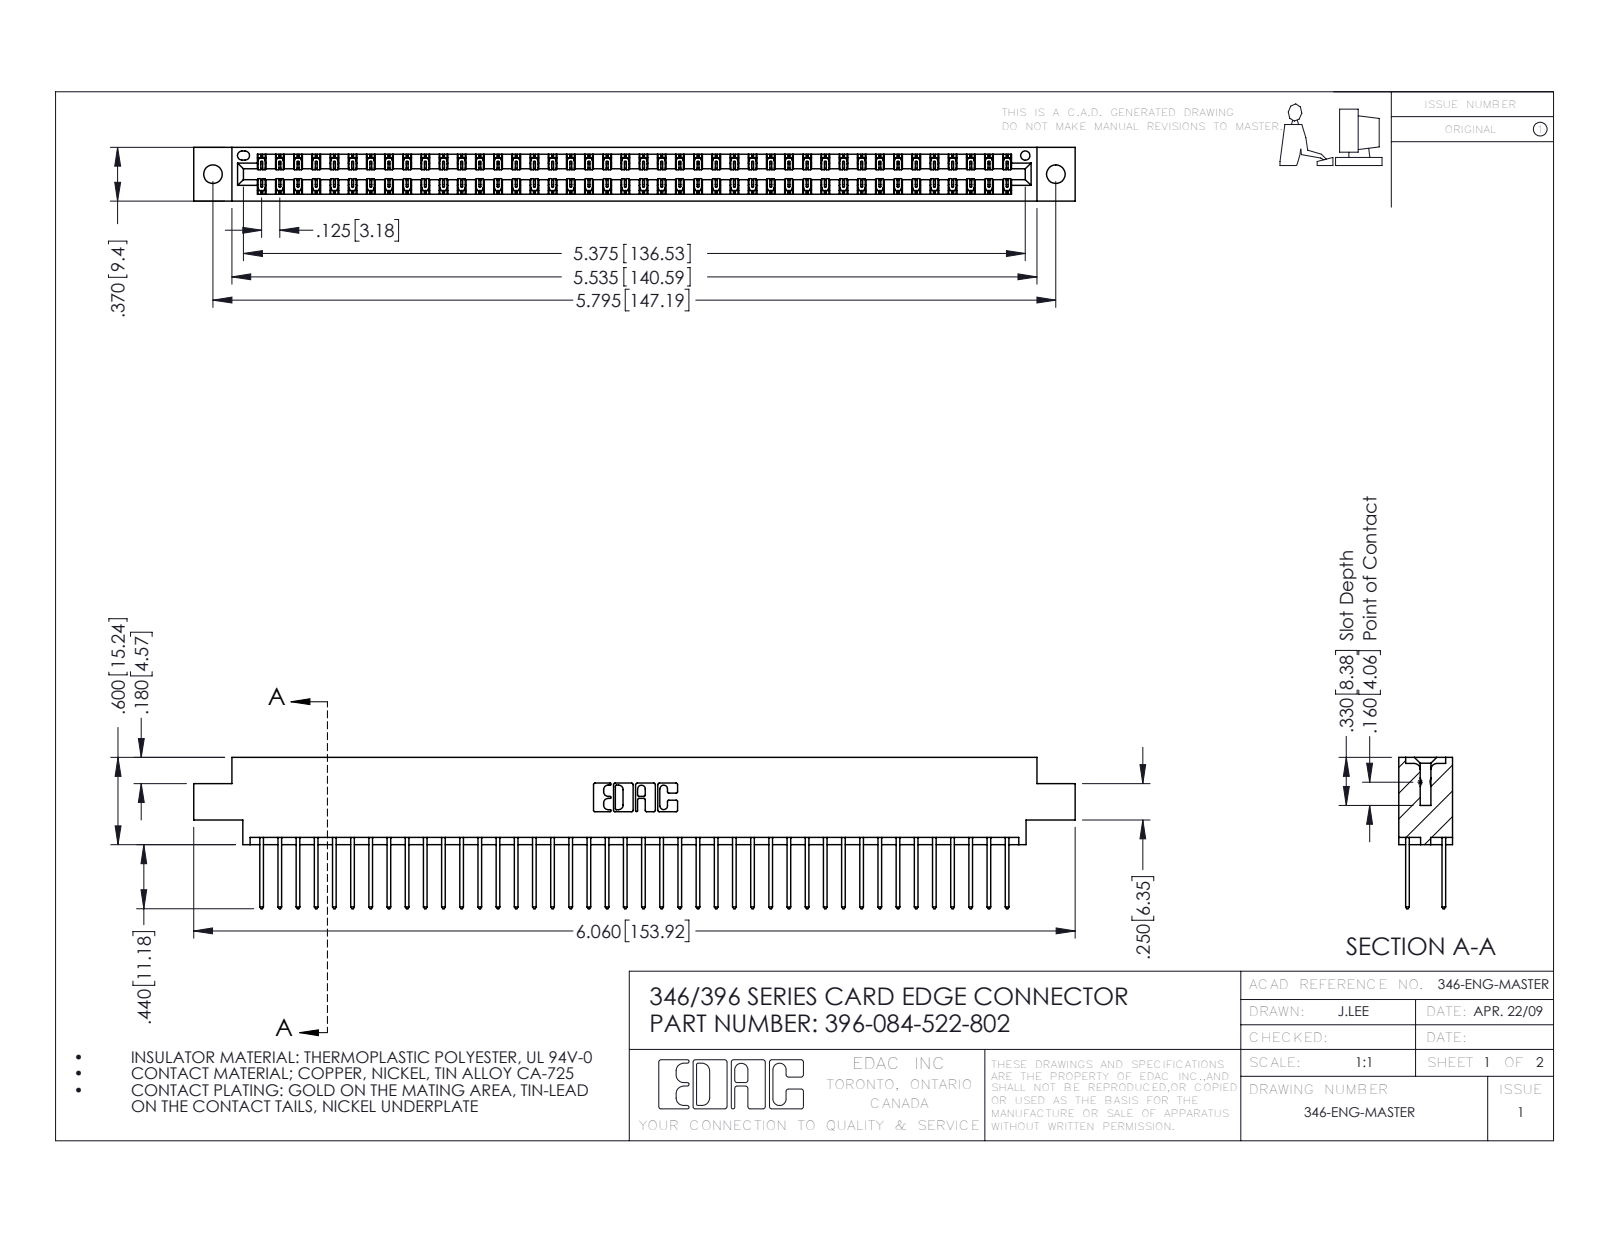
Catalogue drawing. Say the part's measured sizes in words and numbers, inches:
The part is named "345-292-001_345-293-122; 396-084-522-802; 346 Part_0.170 Offset - 0.128 Dia". Its 3-D file was written by "SolidWorks 2016 (CONFIG_CONTROL_DESIGN)". It is 85 solids with 4494 faces: 3020 planar, 1474 cylindrical and 0 other. Overall it measures 6.06 by 1.04 by 0.37 inches. Its volume is 0.917 cubic inches and its surface area 33.44 square inches. Round holes: 2 of diameter 0.128, 1 of diameter 0.064. Partial cylindrical surfaces (rounded edges, fillets, slot ends): 126 of radius 0.006, 84 of radius 0.01, 22 of radius 0.01, 6 of radius 0.007, 6 of radius 0.031, 3 of radius 0.026, 2 of radius 0.014, 2 of radius 0.022. The main face-to-face distances are 0.048, 0.322, 0.25, 0.37, 0.072, 0.298, 0.025, 0.275, 0.148, 0.222. The hole center spacings are 0.246, 5.586, 5.795.
